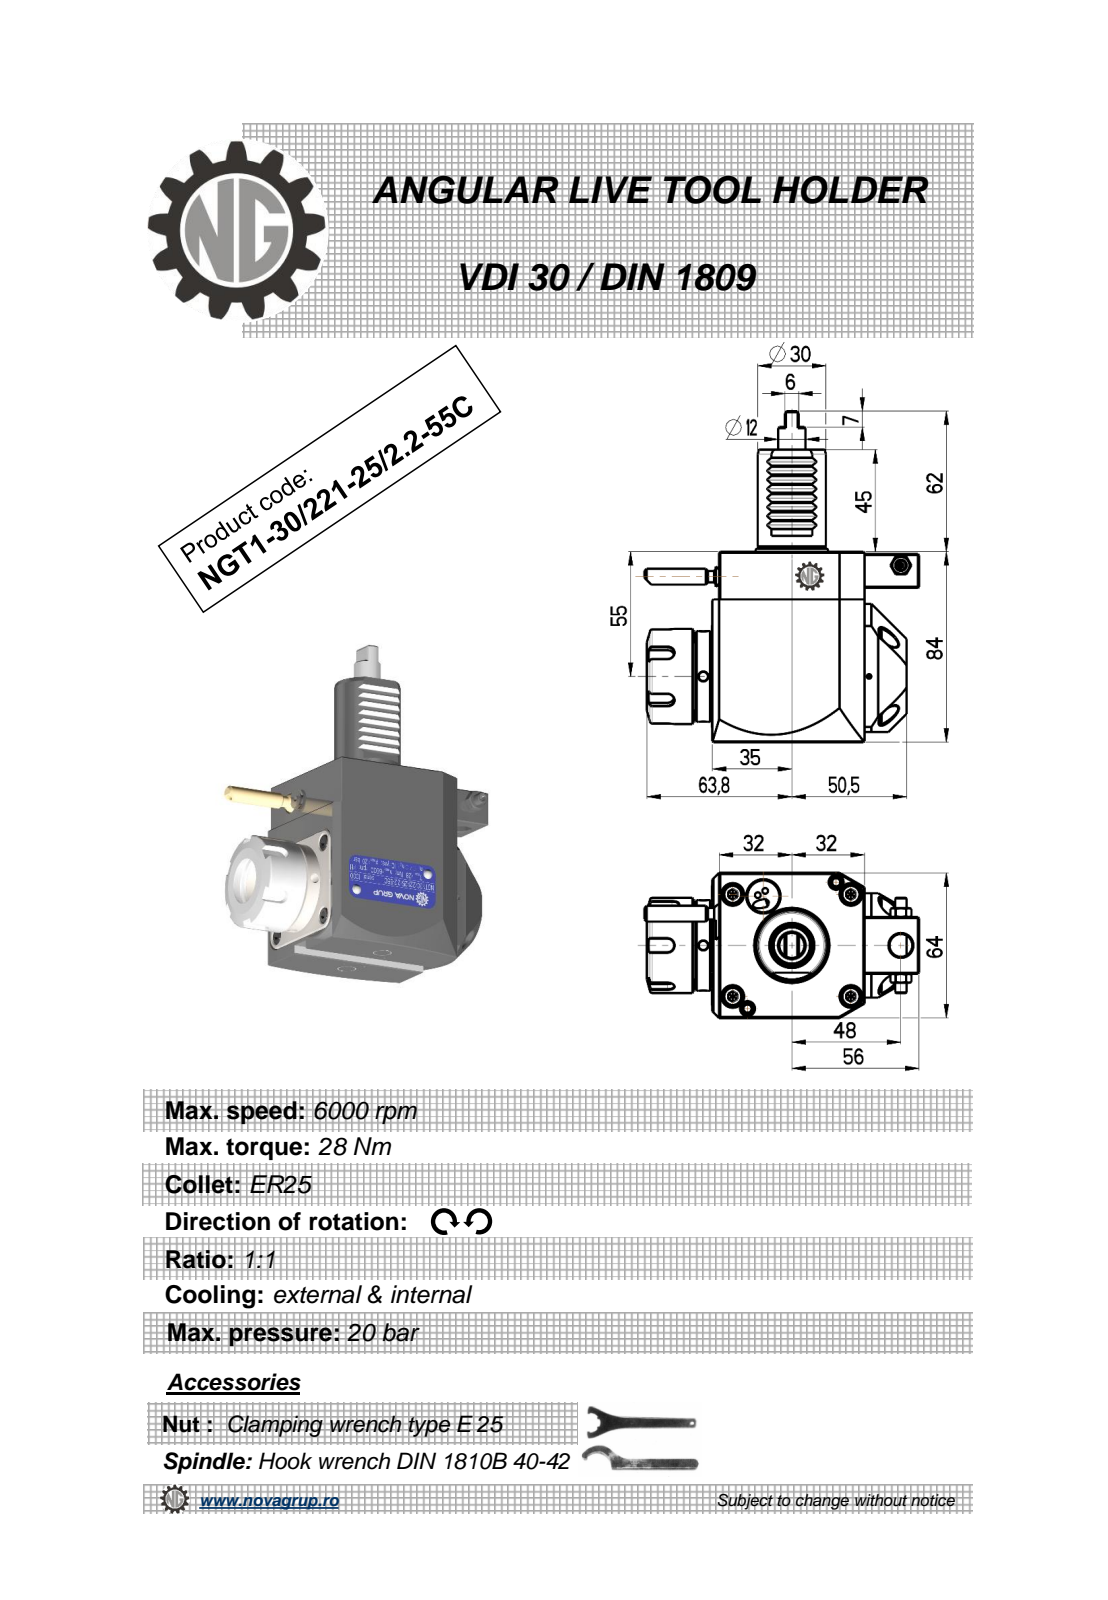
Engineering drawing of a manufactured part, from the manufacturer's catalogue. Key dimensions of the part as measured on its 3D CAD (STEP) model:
Part name (STEP PRODUCT): NGT1_30_221_25_2_2_55C
STEP written by: PRO/ENGINEER BY PARAMETRIC TECHNOLOGY CORPORATION, 2010280 (CONFIG_CONTROL_DESIGN)
Units: millimetres
Bodies: 1 solid, 404 faces (181 planar, 84 cylindrical, 139 other)
Overall size (bounding box): 146 × 120.88 × 65.6
Volume: 454 242 mm³ · Surface area: 46 555 mm²
Round holes (diameter × count): ⌀4 ×2, ⌀2.5 ×1, ⌀3 ×1, ⌀4.2 ×1, ⌀9.5 ×1, ⌀10 ×1, ⌀20.3 ×1
Round bosses / shafts (diameter × count): ⌀8.96 ×2, ⌀5 ×2, ⌀42 ×1, ⌀40 ×1, ⌀33 ×1, ⌀30 ×1, ⌀12 ×1, ⌀7 ×1
Partial cylindrical surfaces — rounded edges, fillets, slot ends (radius × count): R0.26 ×12, R0.3 ×8, R3 ×5, R0.8 ×2, R160 ×2, R32 ×1
Main face-to-face distances: 64, 84, 67.2, 3.2, 3, 67, 0.5, 85.7, 85.5, 82.5
Hole centre spacings: 14.22, 46.17, 46.5, 86.95, 99.81
